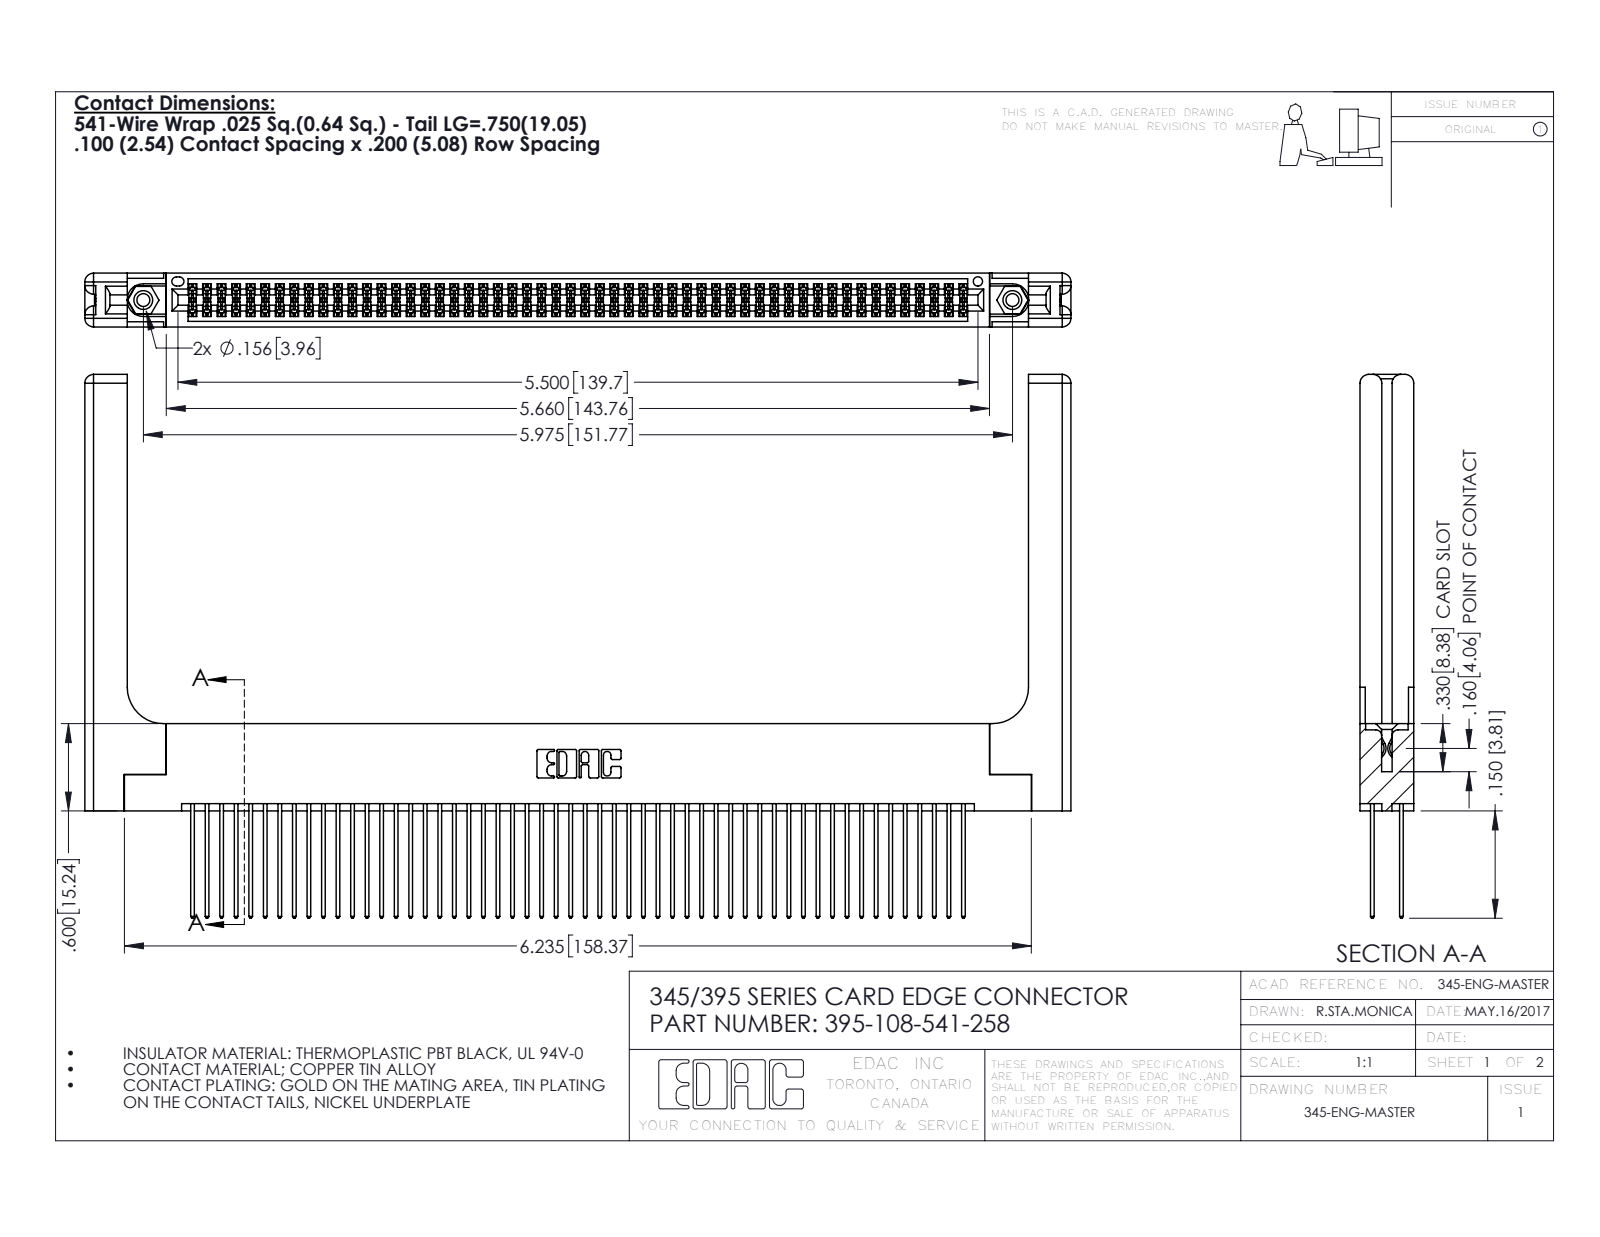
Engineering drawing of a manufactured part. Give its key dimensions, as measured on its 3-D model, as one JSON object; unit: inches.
{"part_name": "345-220-058_345-220-058; 345-292-001_345-293-141; 395-108-541-258; 345 Part_Flush Mounting Lugs - 0.156 Dia-TH (+1 more)", "step_written_by": "SolidWorks 2016 (CONFIG_CONTROL_DESIGN)", "units": "inches", "bodies": {"solids": 113, "faces": 5782, "planar": 3792, "cylindrical": 1930, "other": 60}, "overall_size": [6.779, 3.737, 0.37], "volume_in3": 1.582, "surface_area_in2": 52.71, "round_holes": [[0.089, 2], [0.125, 2], [0.156, 2], [0.064, 1]], "round_bosses_or_shafts": [[0.155, 2]], "partial_cylinders_radius": [[0.006, 162], [0.01, 108], [0.01, 22], [0.06, 16], [0.007, 6], [0.031, 6], [0.026, 3], [0.014, 2]], "face_to_face_distances": [0.072, 0.298, 0.2, 0.098, 0.272, 0.025, 0.37, 0.225, 0.175, 0.148], "hole_center_spacings": [0.27, 5.739, 5.975]}
